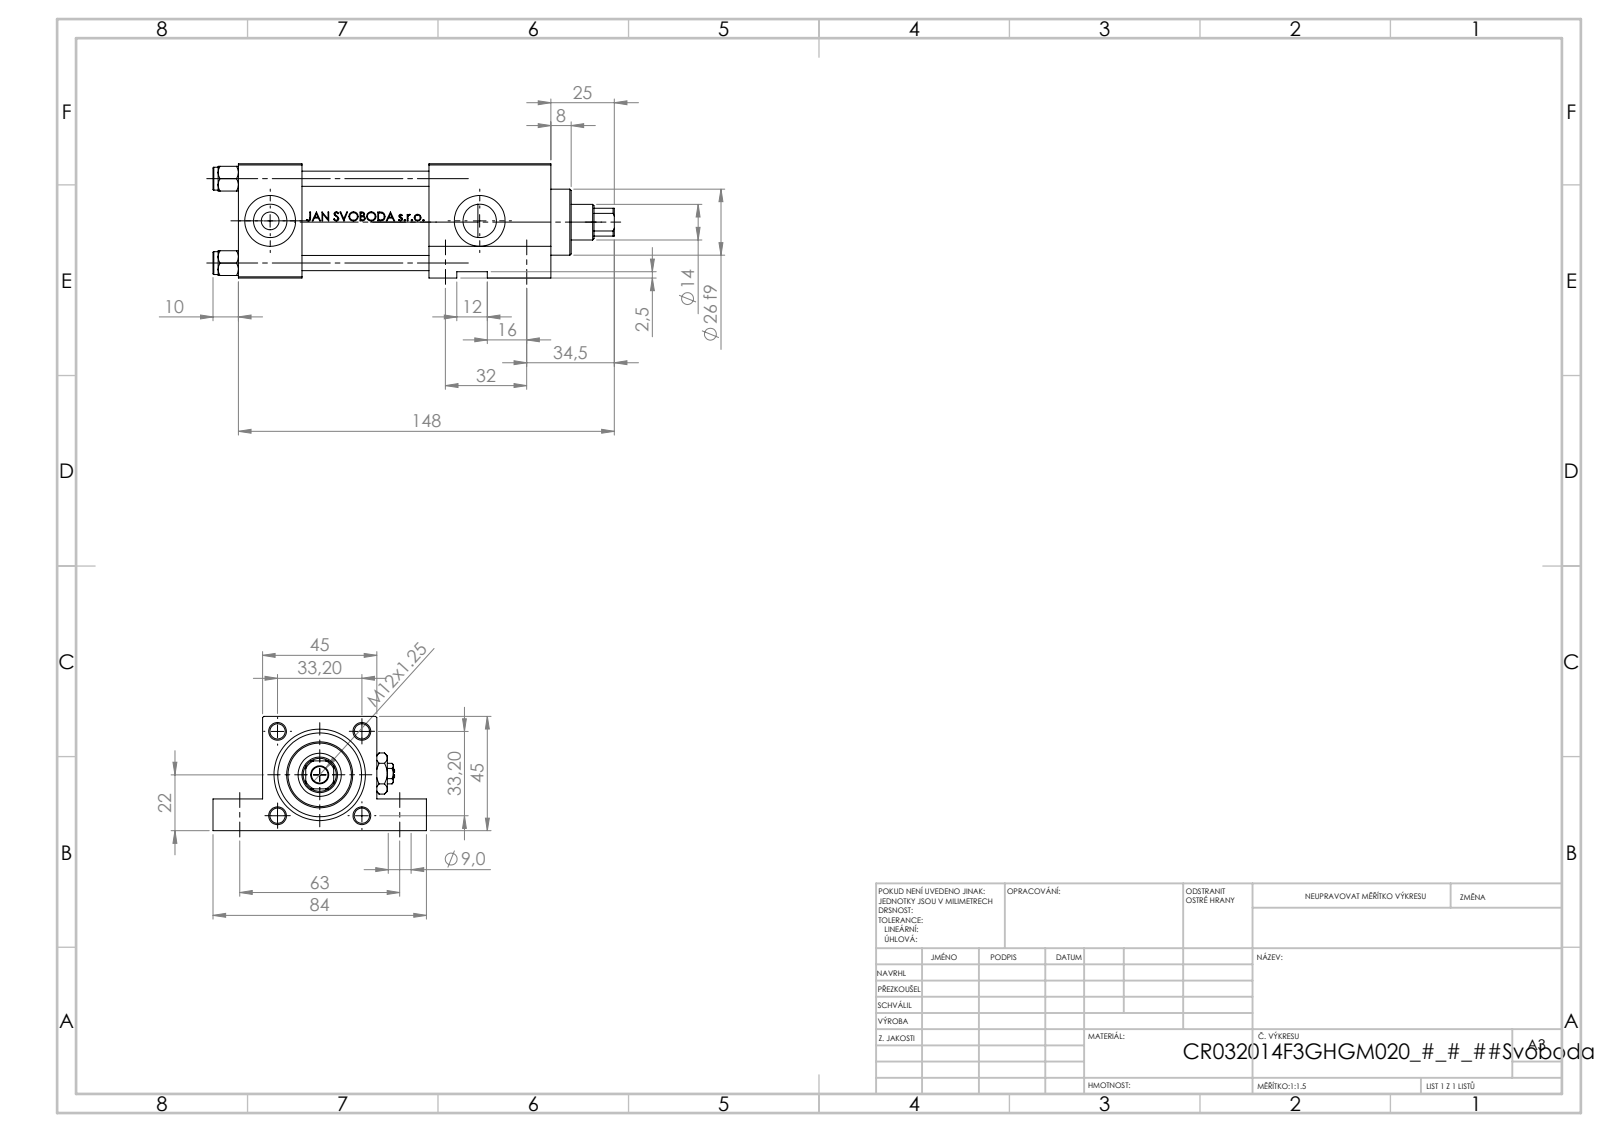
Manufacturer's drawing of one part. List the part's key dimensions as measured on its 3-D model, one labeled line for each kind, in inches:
Part name (STEP PRODUCT): NUT_M5_F; Zatka_pro_OIL_PORT; V215CR_VCP_F; V215CR_F_Body (+2 more)
STEP written by: SolidWorks 2019 (CONFIG_CONTROL_DESIGN)
Units: inches
Bodies: 13 solids, 1198 faces (482 planar, 134 cylindrical, 582 other)
Overall size (bounding box): 6.22 × 3.307 × 1.772
Volume: 12.84 in³ · Surface area: 115.5 in²
Round holes (diameter × count): ⌀0.236 ×4, ⌀0.354 ×4, ⌀0.518 ×3, ⌀0.787 ×3, ⌀0.276 ×2, ⌀0.256 ×1, ⌀0.512 ×1, ⌀0.551 ×1, ⌀0.669 ×1, ⌀0.945 ×1, ⌀1.26 ×1, ⌀1.299 ×1
Round bosses / shafts (diameter × count): ⌀0.354 ×4, ⌀1.496 ×1, ⌀1.024 ×1
Partial cylindrical surfaces — rounded edges, fillets, slot ends (radius × count): R0.256 ×1
Main face-to-face distances: 1.772, 0.984, 3.858, 4.843, 1.969, 1.28, 2.953, 1.89, 0.492, 0.394
Hole centre spacings: 1.307, 0.911, 0.938, 1.26, 1.848, 2.48, 2.782, 0.276
